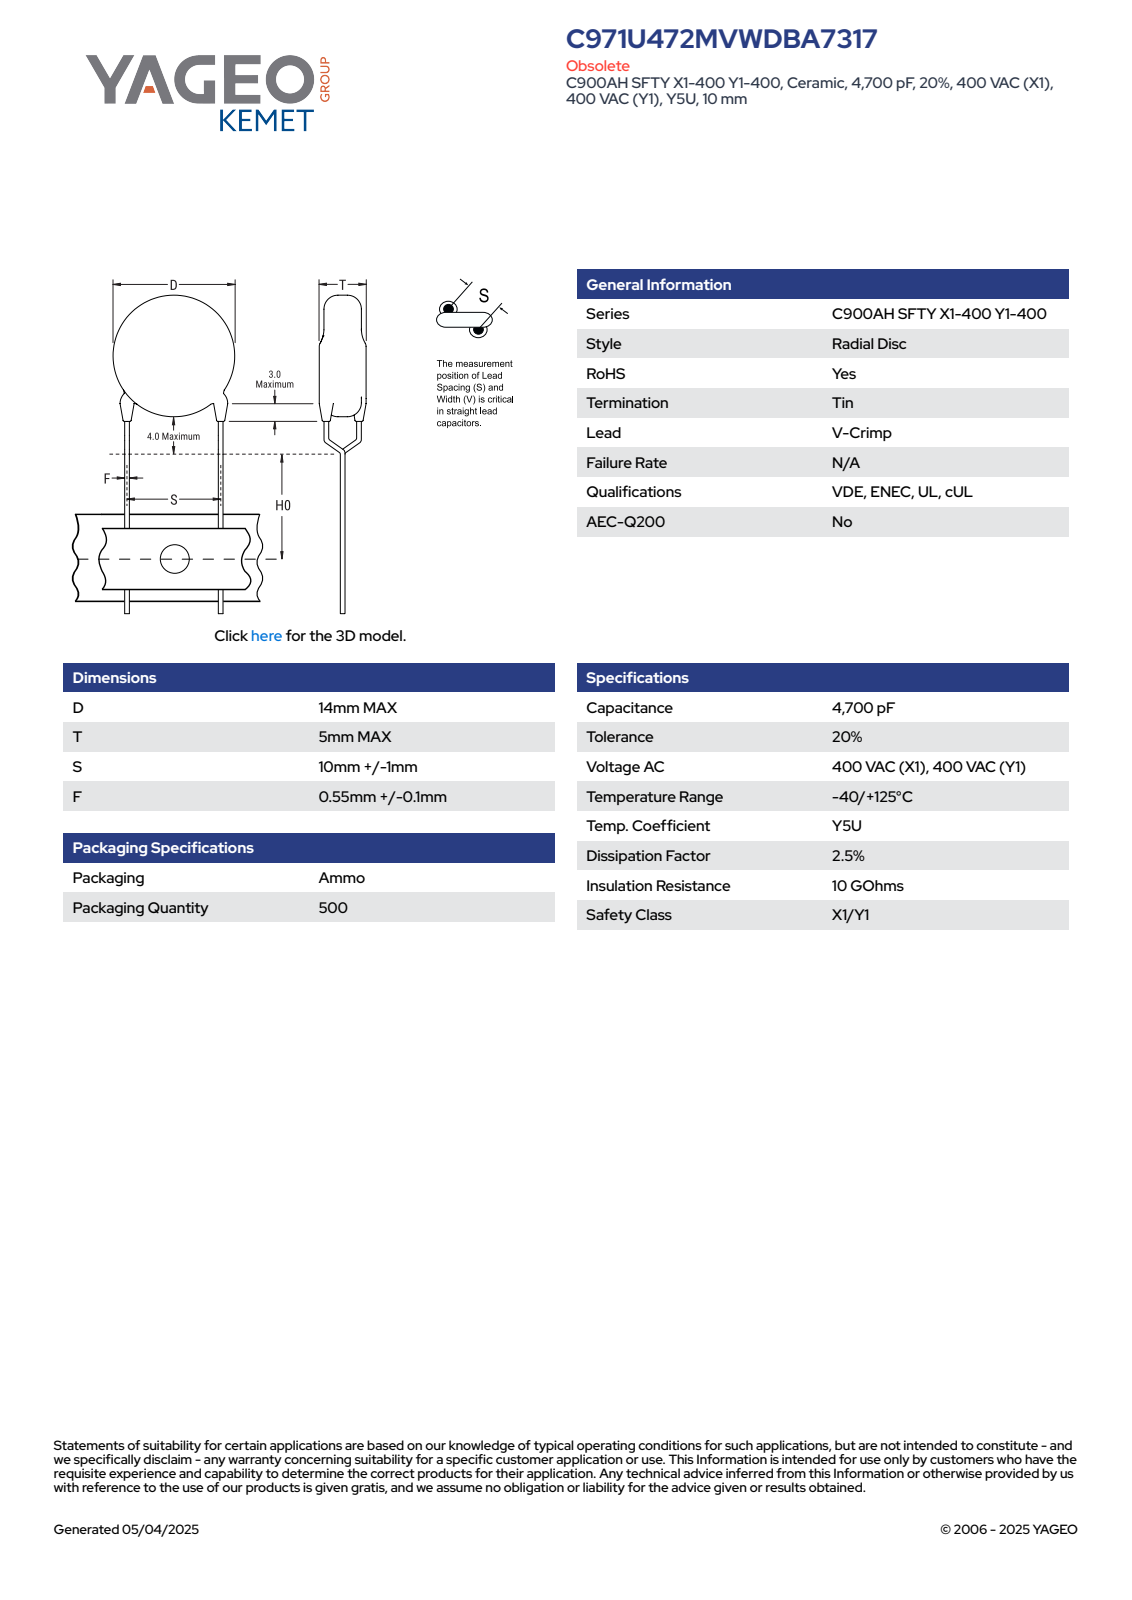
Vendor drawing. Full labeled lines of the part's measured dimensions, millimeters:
Part name (STEP PRODUCT): CCD_VCC900_D14T5S10LL20F0.65
STEP written by: SolidWorks 2014 (AUTOMOTIVE_DESIGN)
Units: millimetres
Bodies: 5 solids, 93 faces (65 planar, 16 cylindrical, 12 other)
Overall size (bounding box): 37.8 × 14 × 5
Volume: 771 mm³ · Surface area: 619 mm²
Round bosses / shafts (diameter × count): ⌀0.65 ×6, ⌀14 ×1
Main face-to-face distances: 5, 22.9, 31.7, 8.8, 29.89, 6.99, 1.81, 0.49, 7.43, 0.35
